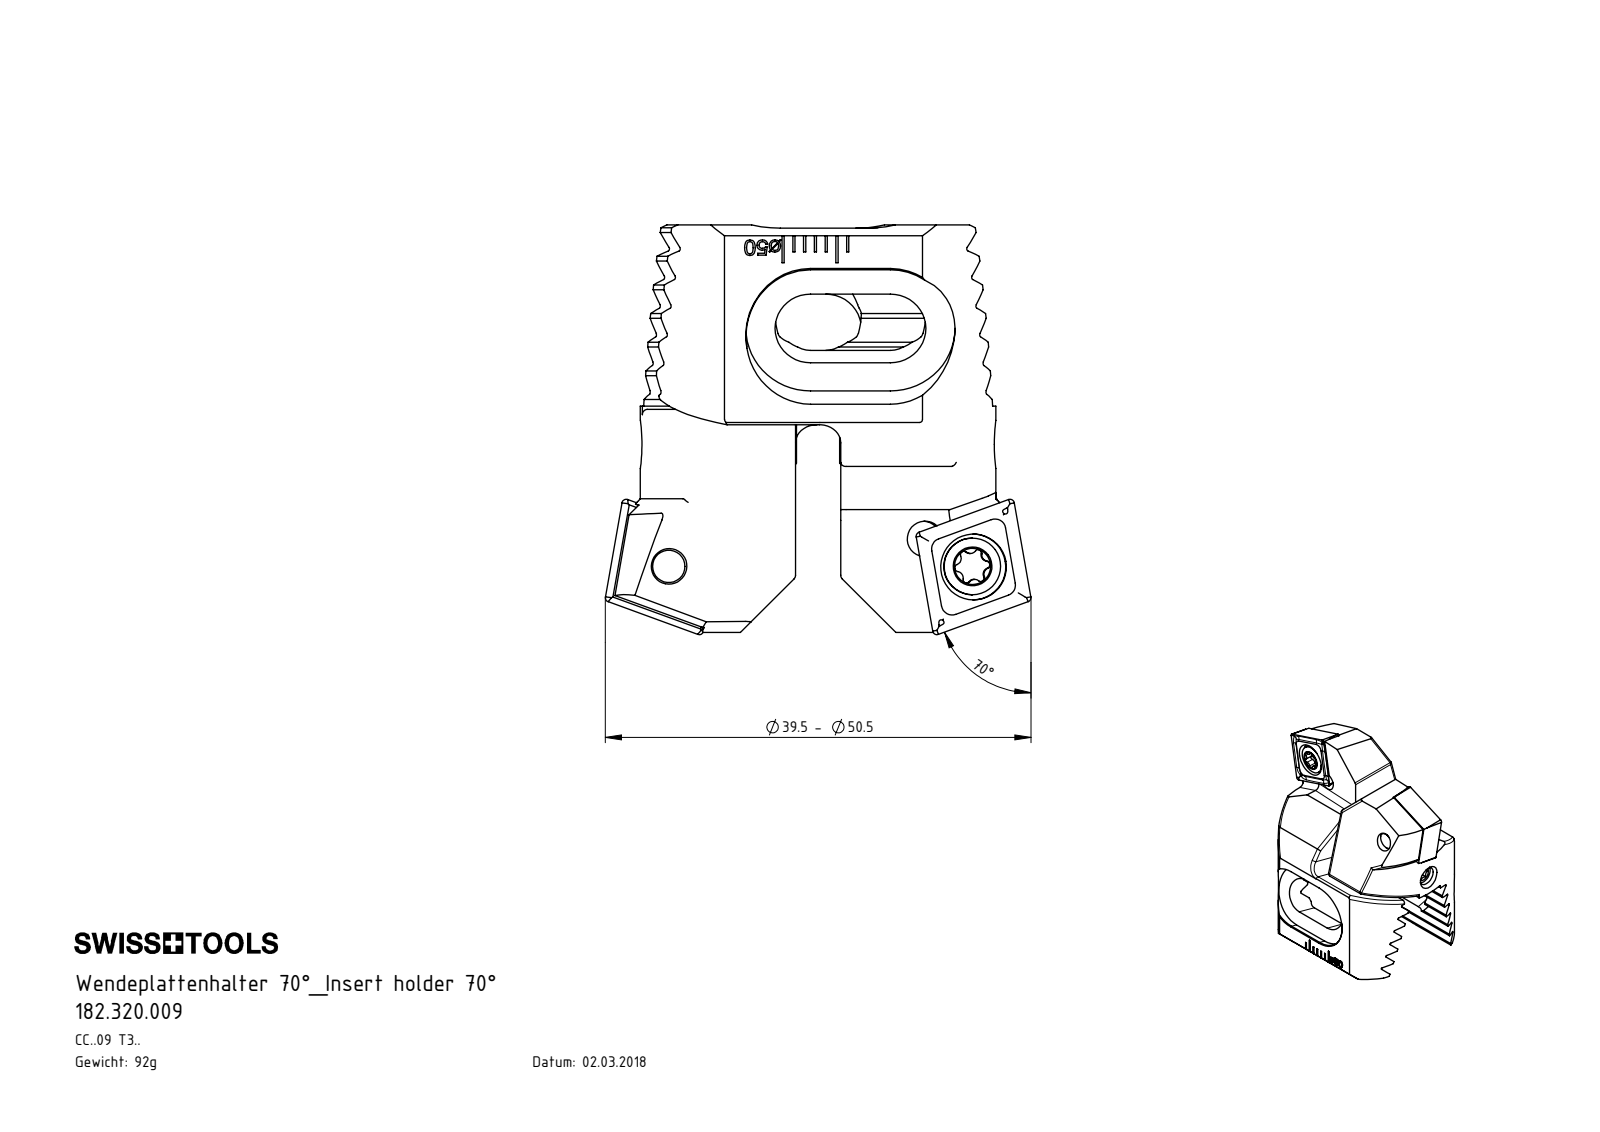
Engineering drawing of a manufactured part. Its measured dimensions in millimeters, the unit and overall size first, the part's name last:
Units: millimetres
Overall size (bounding box): 39.5 × 38 × 26.2
Round holes (diameter × count): ⌀3.3 ×4, ⌀1.6 ×2, ⌀4.4 ×2, ⌀6.1 ×2, ⌀2 ×1, ⌀3.5 ×1
Round bosses / shafts (diameter × count): ⌀4 ×3, ⌀5.25 ×2
Partial cylindrical surfaces — rounded edges, fillets, slot ends (radius × count): R0.5 ×16, R0.2 ×12, R0.34 ×12, R0.59 ×12, R1 ×4, R2 ×4, R3.3 ×4, R6 ×4
Main face-to-face distances: 2.38, 4.76, 9.53, 7.15, 4.89, 11.91, 7.14, 1.27, 4.77, 2.39
Hole centre spacings: 5.09, 5.19, 9, 24.33, 24.42, 28.69, 17.38, 19.79
Volume: 11 747 mm³ · Surface area: 8 192 mm²
Bodies: 8 solids, 648 faces (298 planar, 138 cylindrical, 212 other)
Part name (STEP PRODUCT): 182.320.009; Z32-ER3.001.013_A; Z32-xxx.001.021_B_70ø; WCB-ER2.001.009_A (+1 more)
STEP written by: SolidWorks 2017 (CONFIG_CONTROL_DESIGN)
